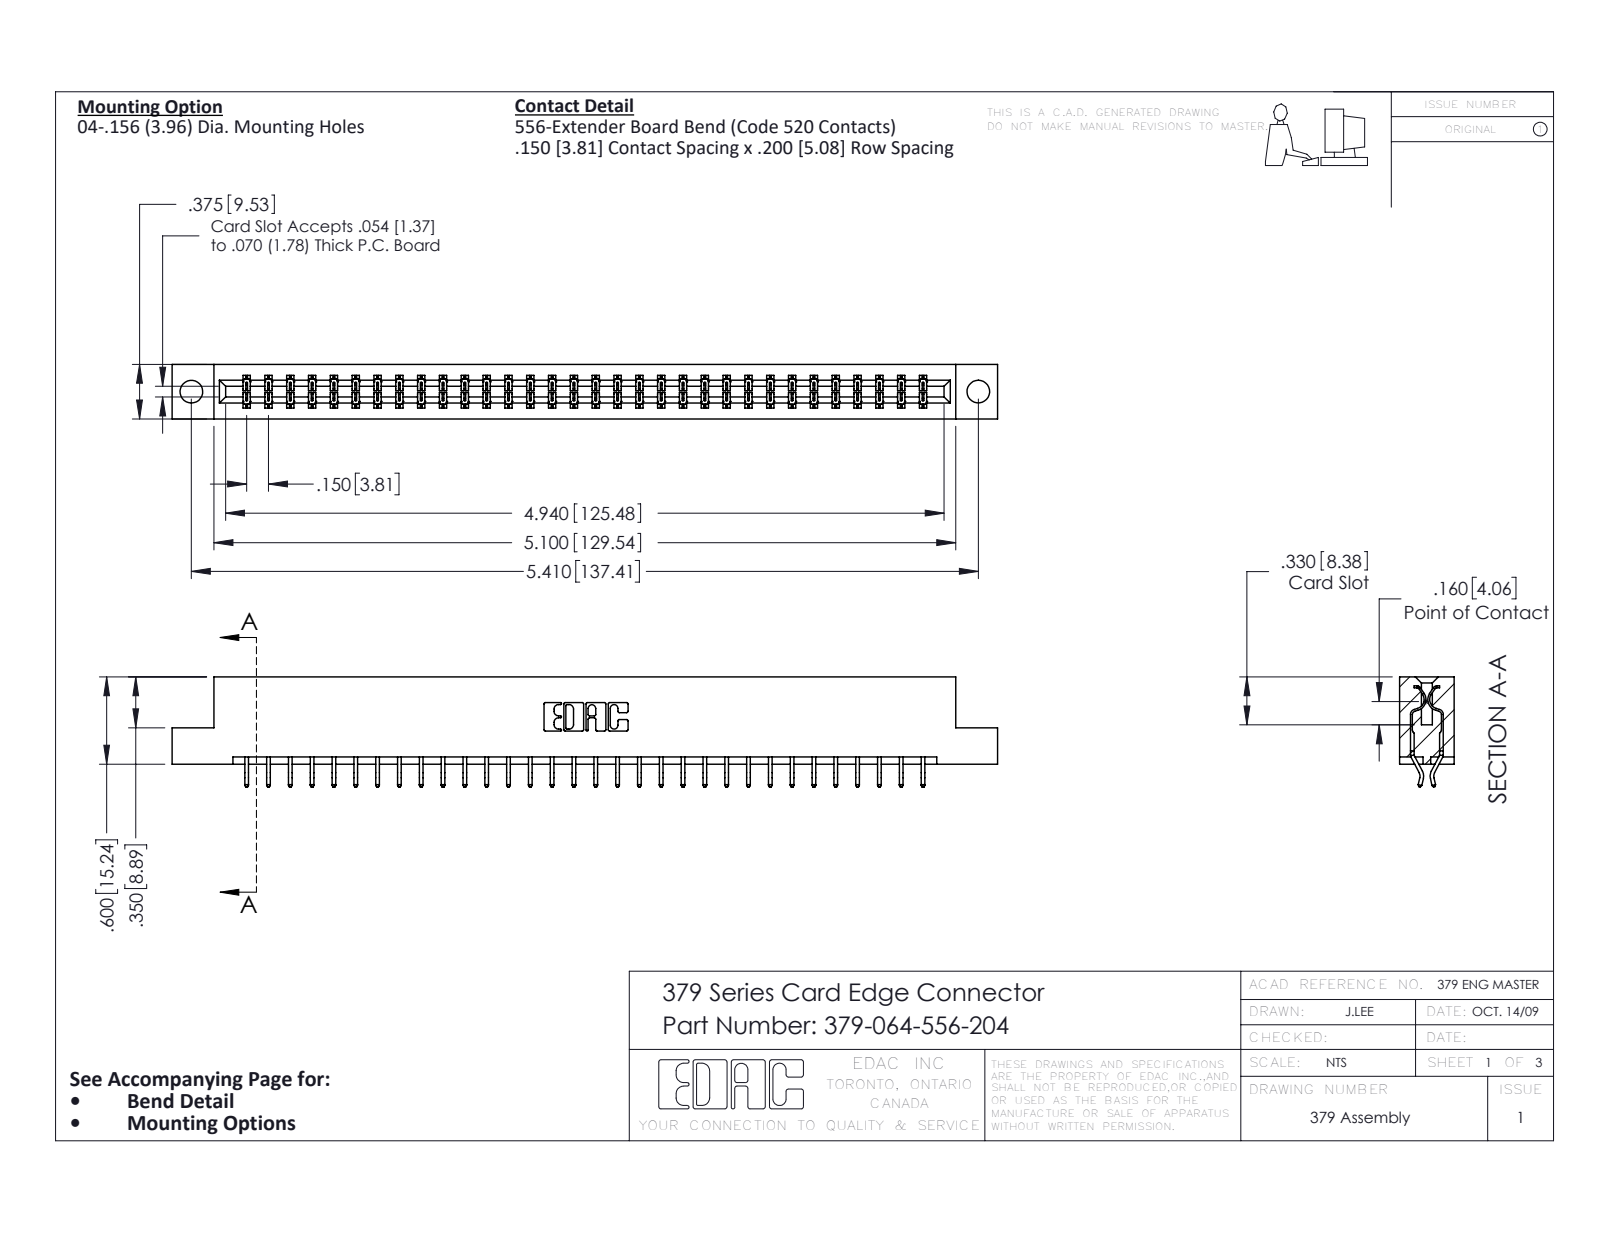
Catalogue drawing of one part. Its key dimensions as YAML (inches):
part_name: "379-064-556-204; 345-292-001_556 Tail; 379 Part_Flush - .156 Dia - TH"
step_written_by: "SolidWorks 2016 (CONFIG_CONTROL_DESIGN)"
units: inches
bodies: {solids: 65, faces: 3826, planar: 2630, cylindrical: 1196, other: 0}
overall_size: [5.675, 0.757, 0.375]
volume: 0.924
surface_area: 25.8
round_holes:
  - {diameter: 0.156, count: 2}
partial_cylinders:
  - {radius: 0.006, count: 96}
  - {radius: 0.01, count: 22}
  - {radius: 0.007, count: 6}
  - {radius: 0.031, count: 6}
  - {radius: 0.026, count: 3}
  - {radius: 0.01, count: 2}
  - {radius: 0.014, count: 2}
  - {radius: 0.022, count: 2}
face_to_face_distances: [0.3, 0.075, 0.375, 0.225, 0.6, 0.15, 0.076, 0.2, 0.025, 0.275]
hole_center_spacings: [5.41]
